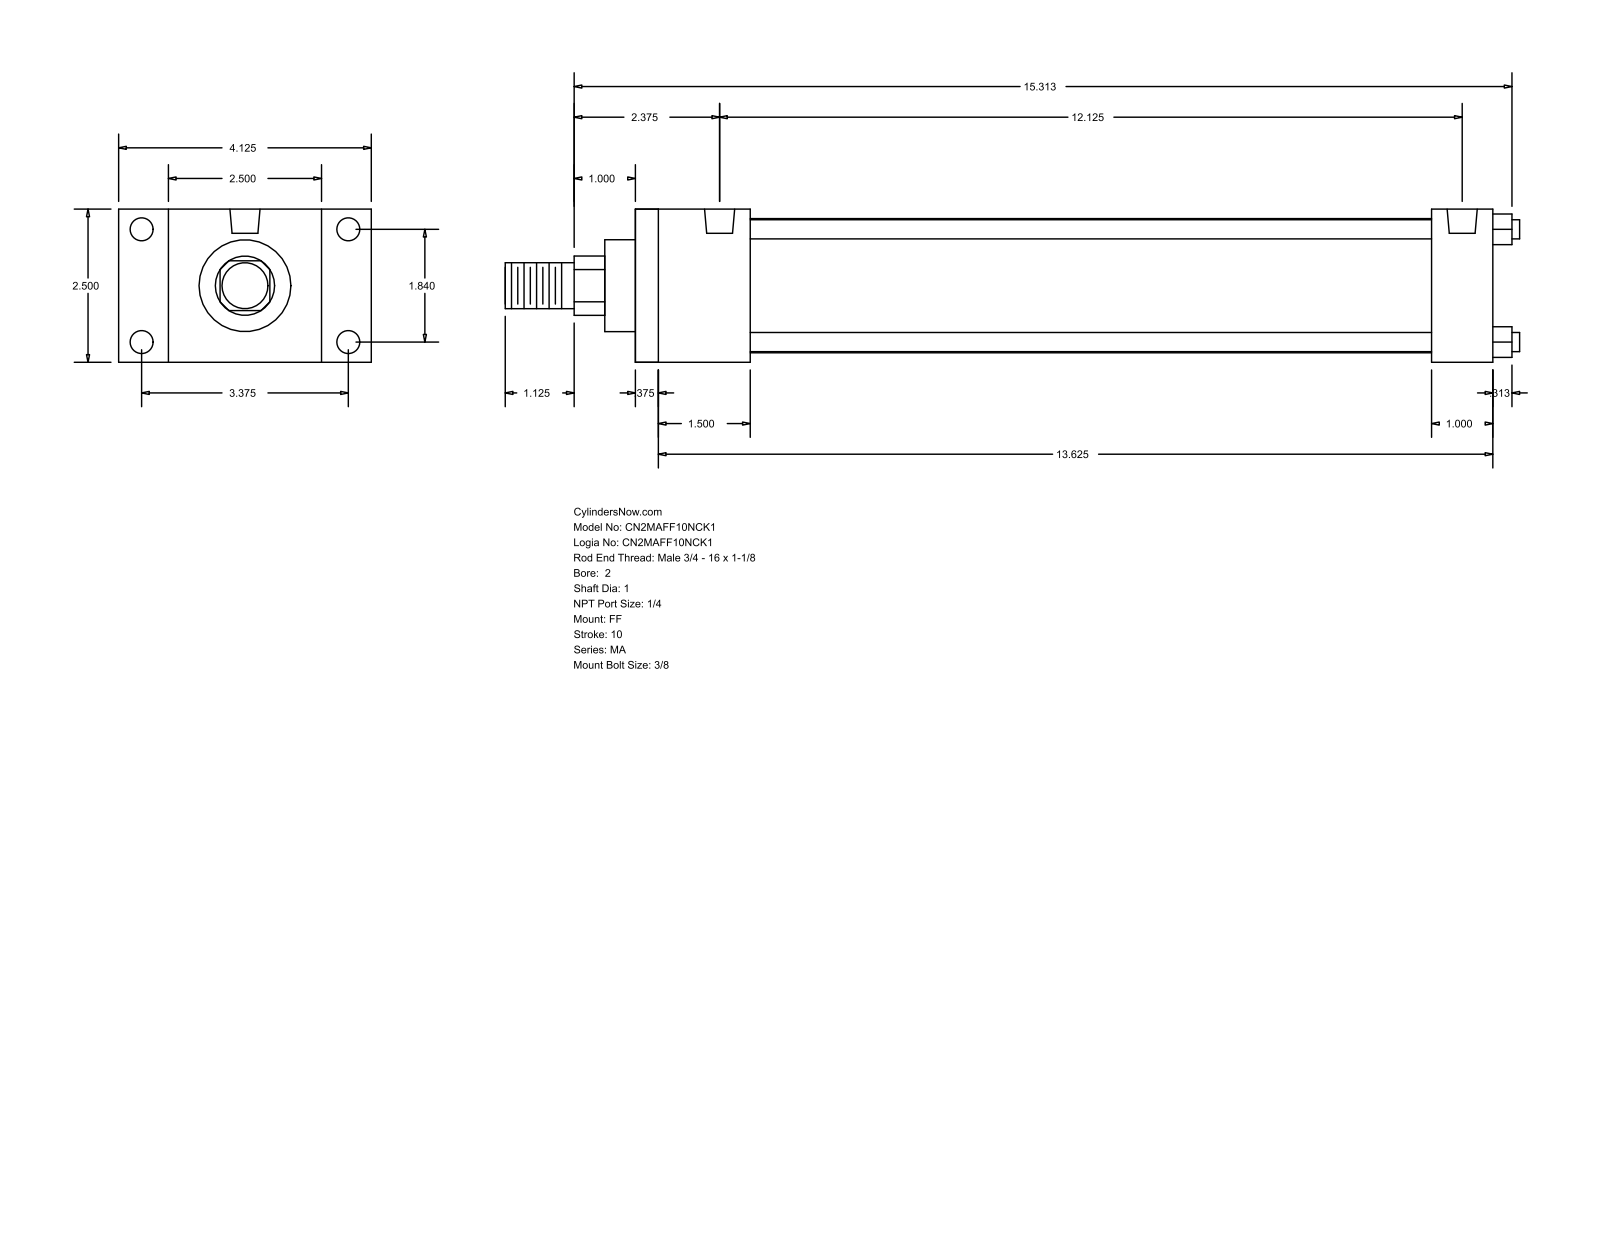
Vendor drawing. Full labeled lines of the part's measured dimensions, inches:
Part name (STEP PRODUCT): MA_FF__0200_1
STEP written by: GSSL Pune (CONFIG_CONTROL_DESIGN)
Units: inches
Bodies: 0 solids, 92 faces (64 planar, 28 cylindrical, 0 other)
Overall size (bounding box): 16.563 × 4.125 × 2.5
Round holes (diameter × count): ⌀0.313 ×4, ⌀0.375 ×4, ⌀0.492 ×2
Round bosses / shafts (diameter × count): ⌀0.313 ×4, ⌀2.19 ×1, ⌀1.5 ×1, ⌀1 ×1, ⌀0.75 ×1
Partial cylindrical surfaces — rounded edges, fillets, slot ends (radius × count): R0.484 ×1
Main face-to-face distances: 2.5, 14, 0.375, 13.625, 1, 0.813, 0.5, 1.875, 13, 1.5
Hole centre spacings: 1.84, 3.375, 3.844, 12.125
